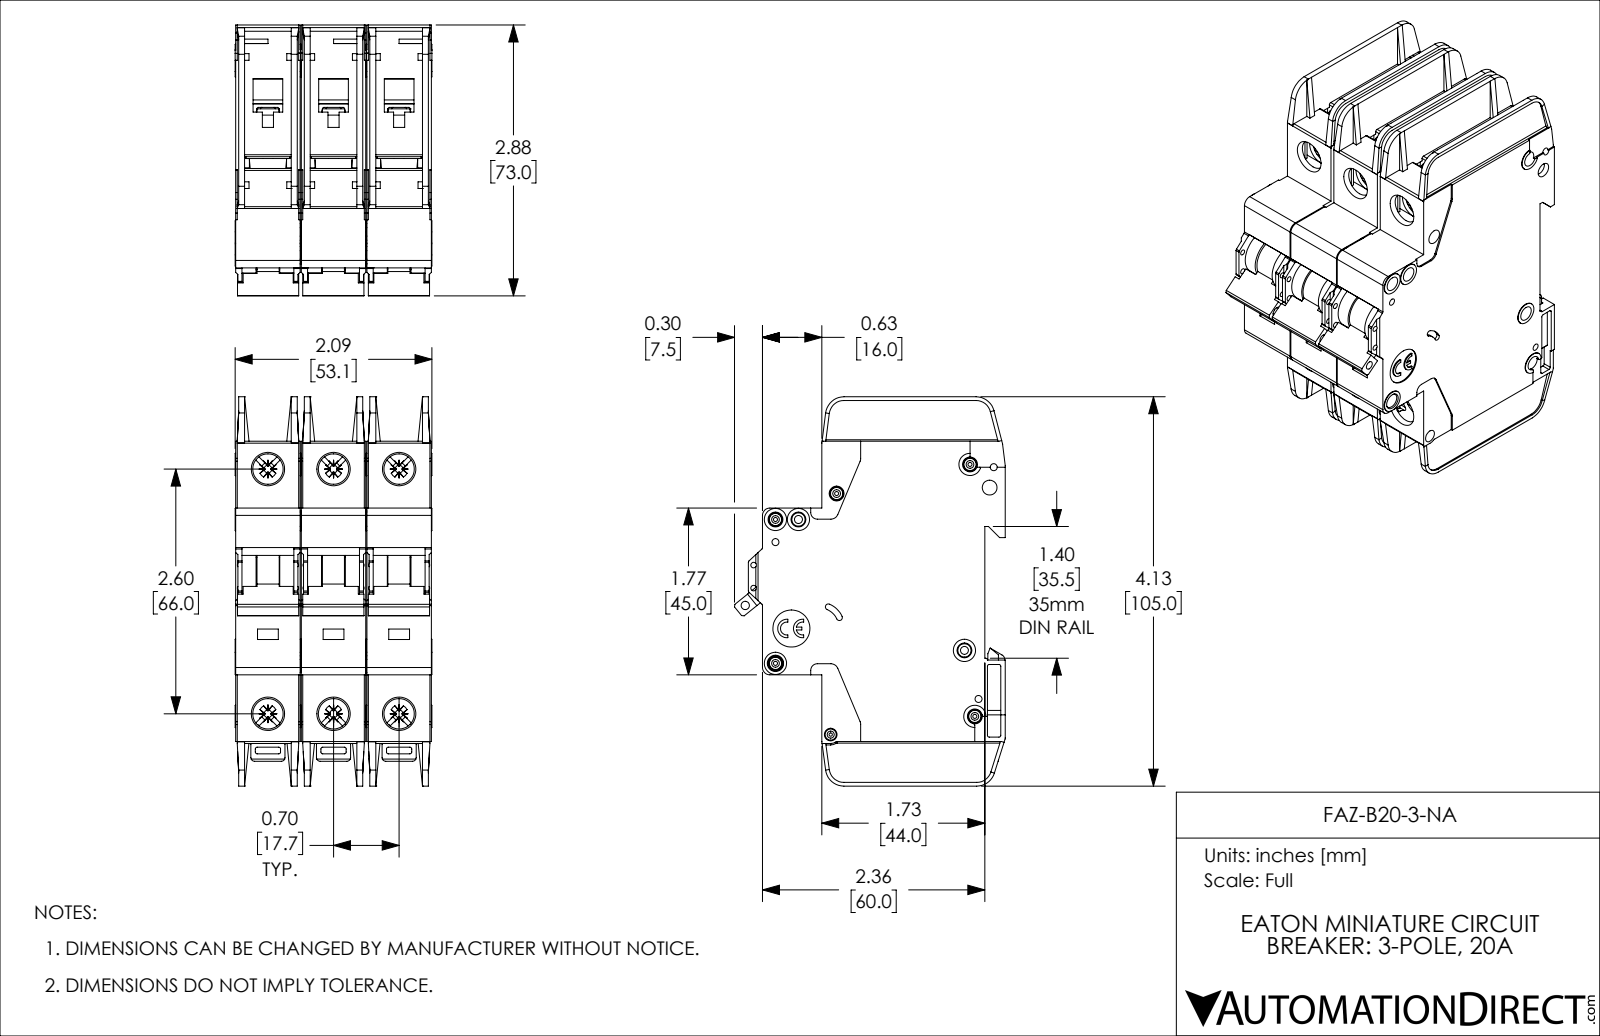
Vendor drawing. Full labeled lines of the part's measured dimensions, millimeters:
Part name (STEP PRODUCT): FAZ-B20-3-NA
STEP written by: SolidWorks 2019 (AUTOMOTIVE_DESIGN)
Units: millimetres
Bodies: 3 solids, 3381 faces (2013 planar, 1071 cylindrical, 297 other)
Overall size (bounding box): 105 × 73.1 × 53.1
Volume: 230 200 mm³ · Surface area: 79 350 mm²
Round holes (diameter × count): ⌀4 ×8, ⌀8.2 ×6, ⌀1.1 ×5, ⌀1.9 ×4, ⌀1.5 ×2, ⌀2.2 ×2, ⌀0.9 ×1, ⌀2.3 ×1, ⌀2.5 ×1, ⌀3.4 ×1, ⌀10 ×1
Round bosses / shafts (diameter × count): ⌀3.3 ×5, ⌀6 ×4, ⌀3 ×4, ⌀2.5 ×3
Partial cylindrical surfaces — rounded edges, fillets, slot ends (radius × count): R0.5 ×72, R0.4 ×30, R1 ×18, R1.1 ×12, R2 ×12, R0.2 ×6, R0.3 ×6, R0.7 ×6
Main face-to-face distances: 17.7, 1.2, 35.4, 17.4, 15, 35.1, 18.9, 16.5, 2.7, 2.4
Hole centre spacings: 17.7, 68.3, 66, 6.2, 13.6, 22.1, 35.4, 74.9
